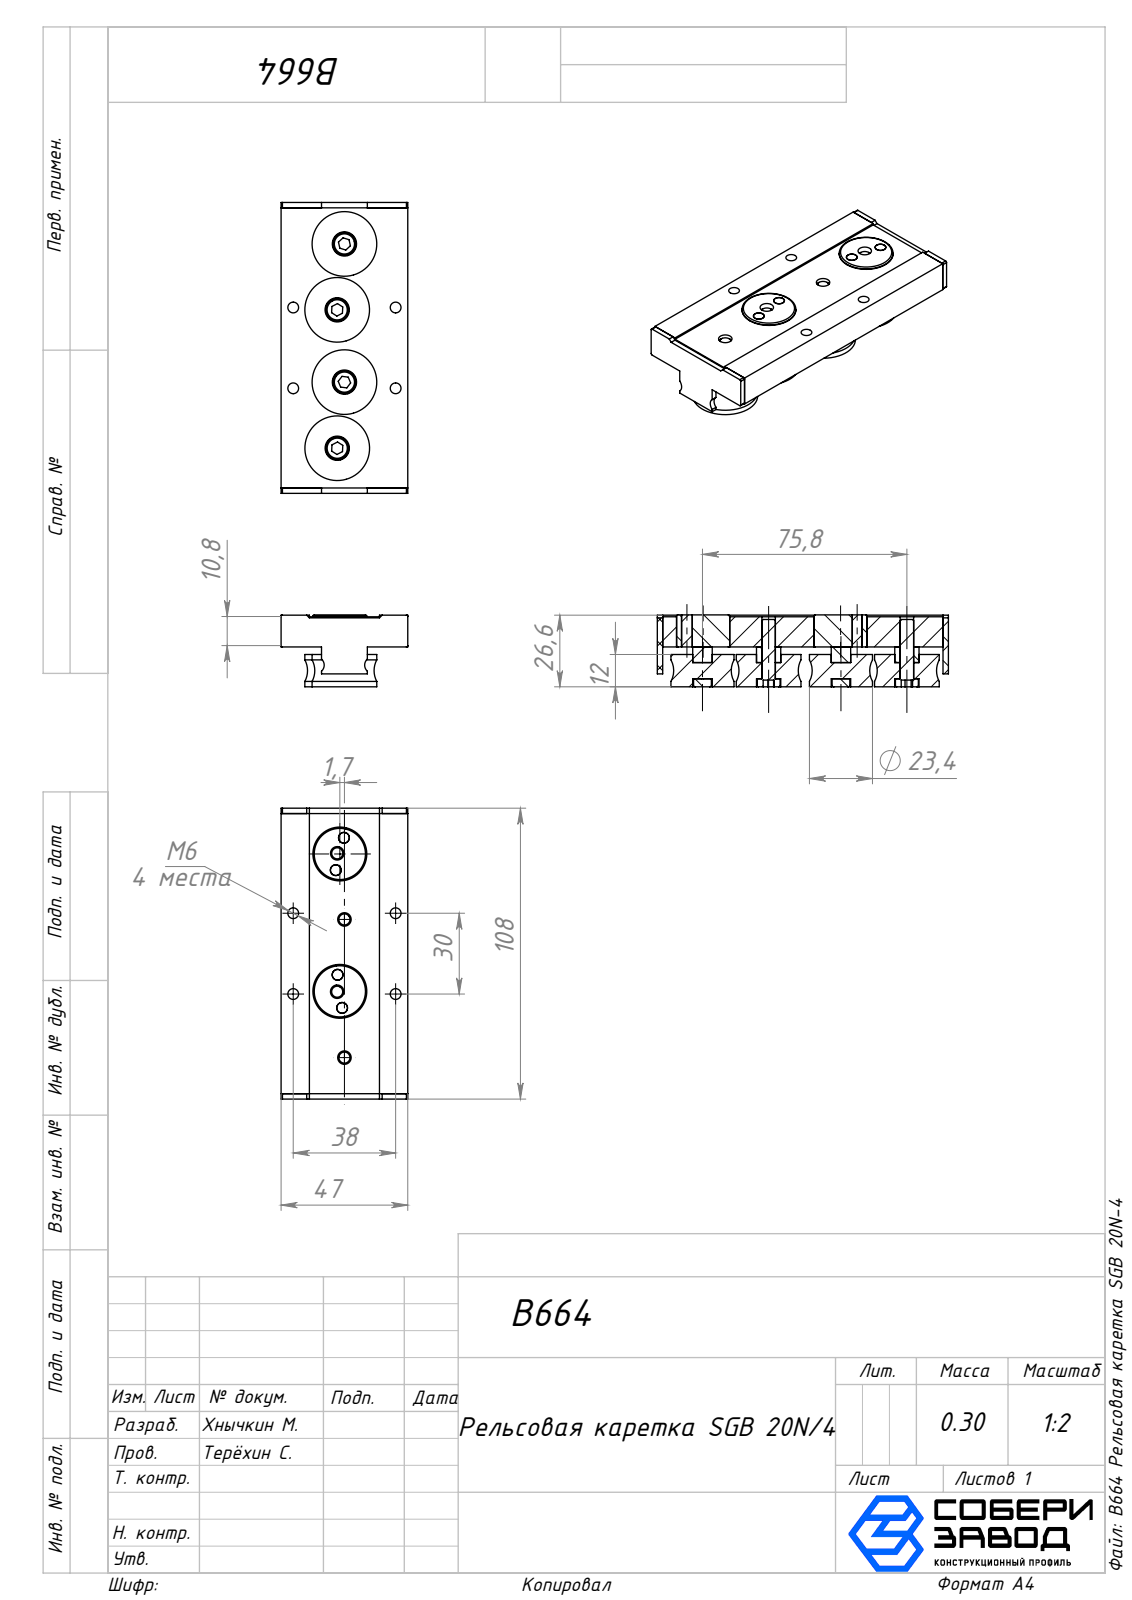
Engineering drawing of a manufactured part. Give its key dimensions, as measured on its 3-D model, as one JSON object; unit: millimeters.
{"part_name": "Каретка_00; B664 Дистанционная втулка_00; B664 Заслонка_00; B664 Рельсовая каретка SGB 20N-4 (+3 more)", "step_written_by": "SolidWorks 2025 (AUTOMOTIVE_DESIGN)", "units": "millimeters", "bodies": {"solids": 21, "faces": 292, "planar": 118, "cylindrical": 126, "other": 48}, "overall_size": [108, 47, 26.7], "volume_mm3": 79168, "surface_area_mm2": 33578, "round_holes": [[4, 8], [5, 4], [9, 4], [20, 2]], "round_bosses_or_shafts": [[24, 4], [8.5, 4]], "partial_cylinders_radius": [[0.5, 4], [3.03, 2]], "face_to_face_distances": [11.8, 0.6, 11.2, 26, 26.6, 14.8, 14.6, 14, 2.8, 12], "hole_center_spacings": [6.28, 1, 6.2, 6.21, 19.14, 30, 30.3, 33.59]}
